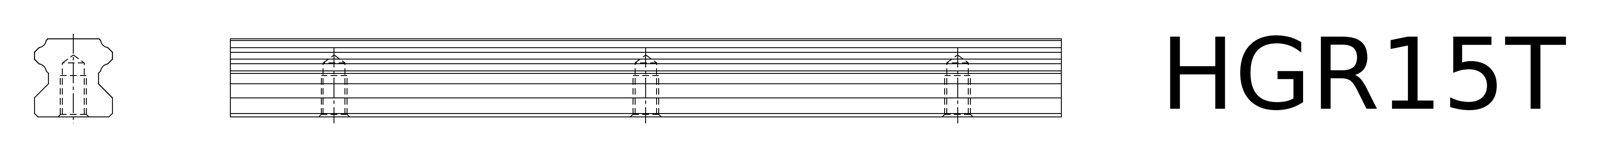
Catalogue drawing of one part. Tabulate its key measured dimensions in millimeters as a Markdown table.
| quantity | value |
| --- | --- |
| part name | HGR15T |
| STEP written by | SolidWorks 2006104 (CONFIG_CONTROL_DESIGN) |
| units | millimeters |
| bodies | 1 solid, 45 faces (25 planar, 20 cylindrical, 0 other) |
| overall size | 150 × 15 × 15 |
| volume | 28 143 mm³ |
| surface area | 9 977 mm² |
| round holes (diameter × count) | 5 × 3 |
| partial cylindrical surfaces (radius × count) | 0.4 × 8, 1.62 × 4, 1 × 2 |
| main face-to-face distances | 15, 2.73, 12.27, 5.4, 11.69, 6.29, 7.29, 12.69, 18.98, 9.54 |
| hole center spacings | 60, 120 |
